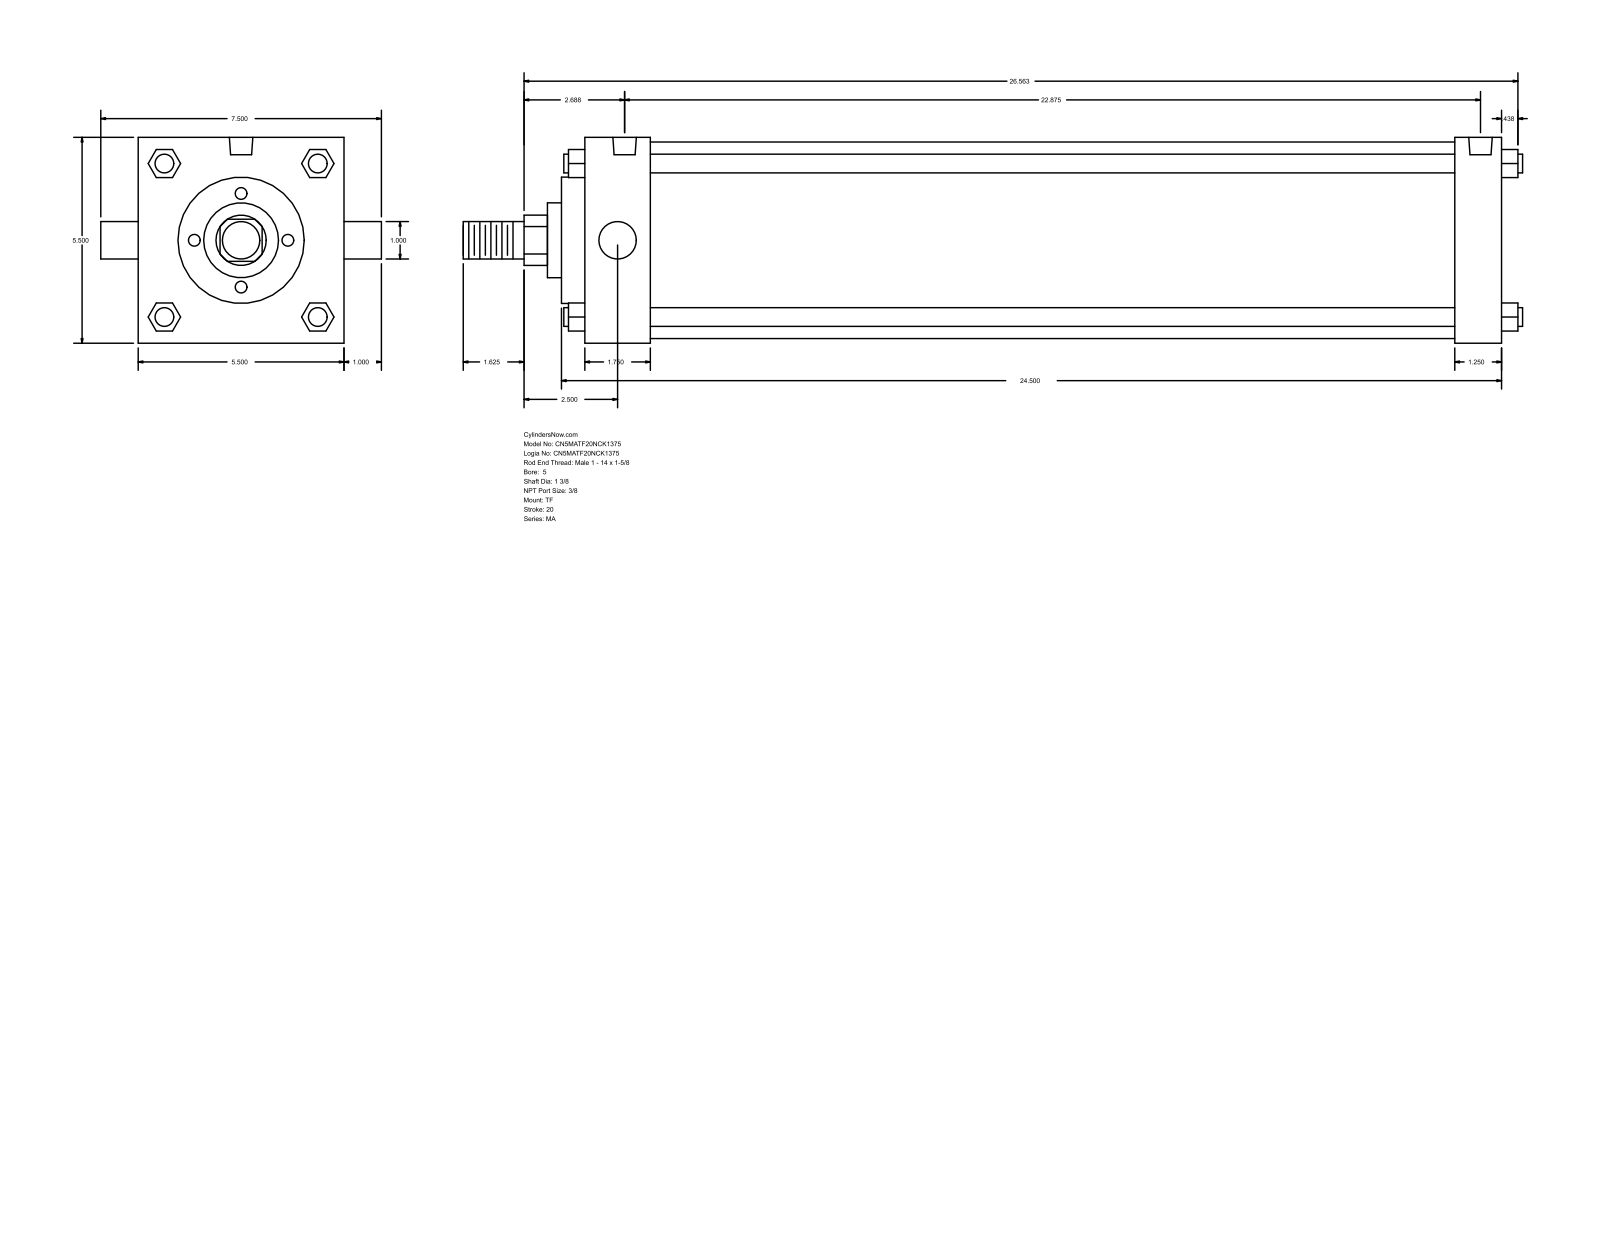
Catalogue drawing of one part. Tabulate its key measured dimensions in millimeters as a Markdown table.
| quantity | value |
| --- | --- |
| part name | MA_TF__0500_1.375 |
| STEP written by | GSSL Pune (CONFIG_CONTROL_DESIGN) |
| units | millimeters |
| bodies | 0 solids, 122 faces (93 planar, 29 cylindrical, 0 other) |
| overall size | 719.14 × 190.5 × 139.7 |
| round holes (diameter × count) | 11.11 × 3, 15.93 × 2 |
| round bosses / shafts (diameter × count) | 12.7 × 4, 25.4 × 2, 133.35 × 1, 85.72 × 1, 50.8 × 1, 34.92 × 1 |
| partial cylindrical surfaces (radius × count) | 17.06 × 1 |
| main face-to-face distances | 139.7, 622.31, 590.56, 31.75, 44.45, 546.11, 577.86, 15.87, 60.32, 606.43 |
| hole center spacings | 4.77, 576.26, 571.49, 581.03 |
